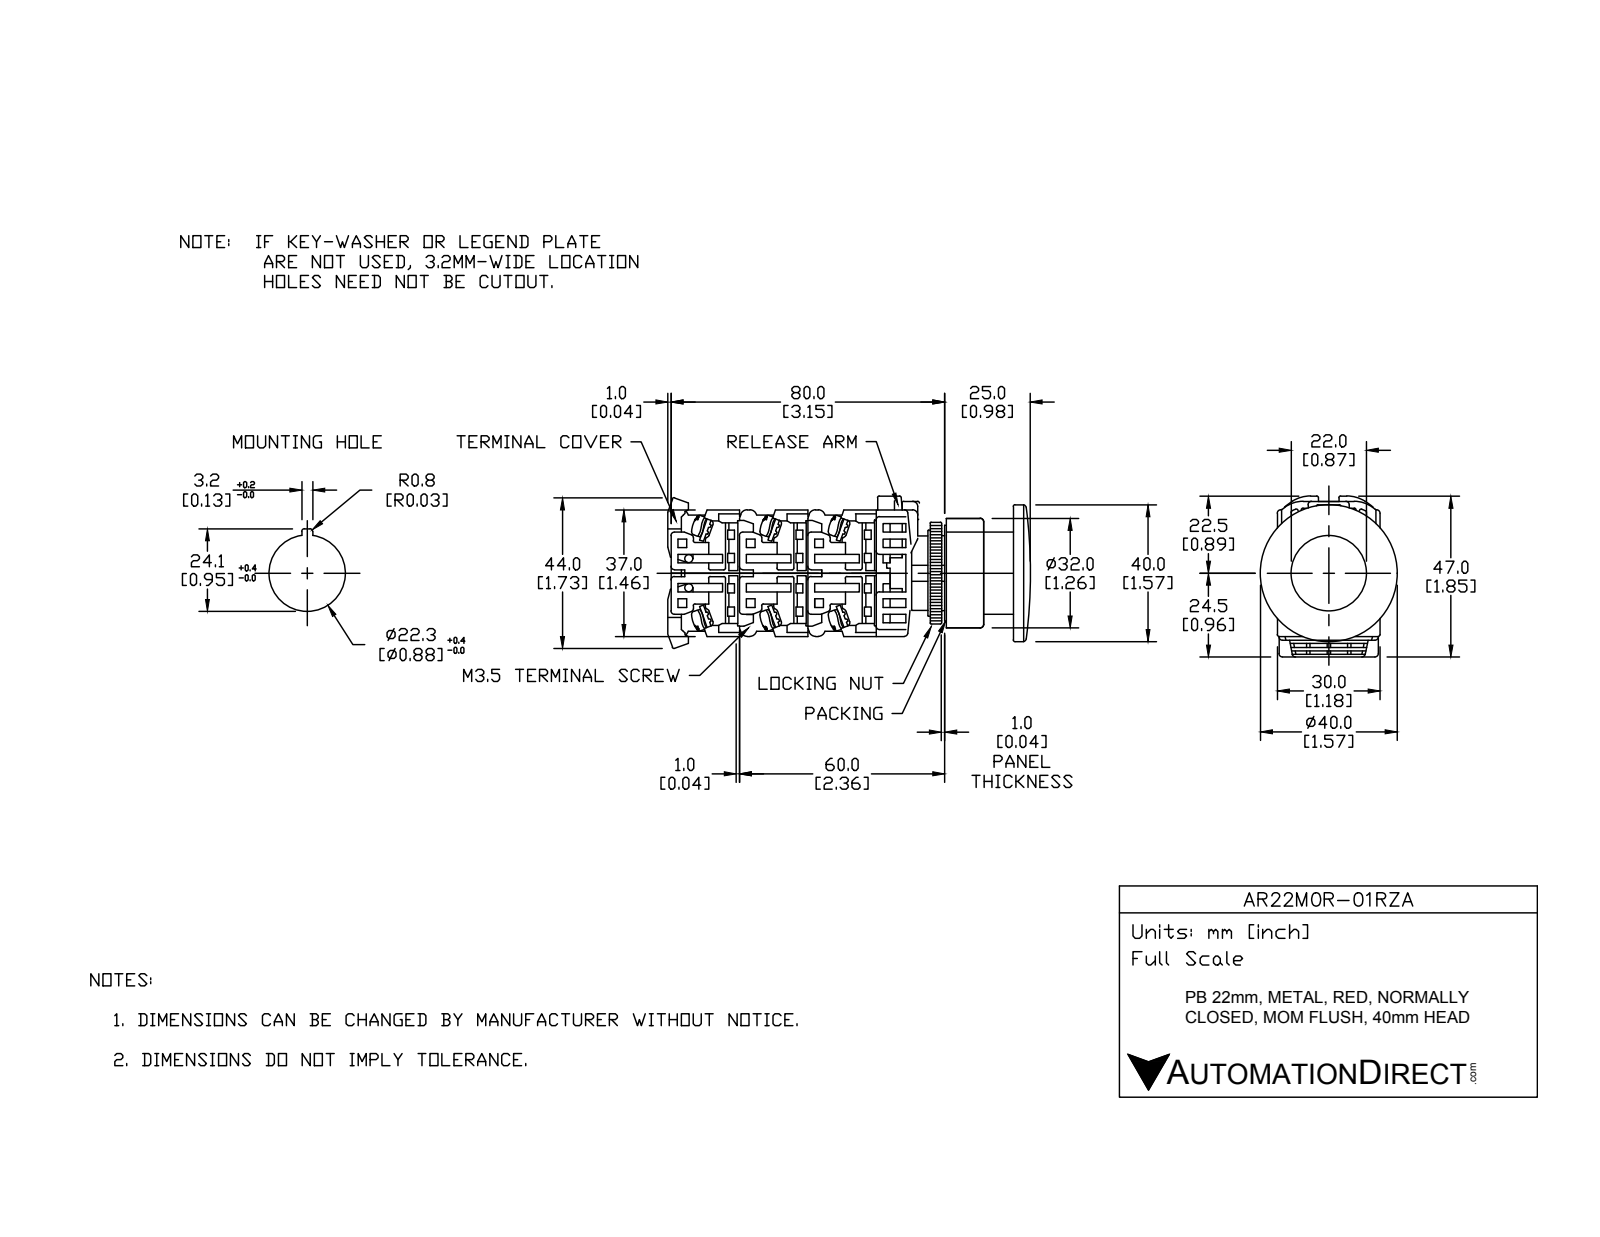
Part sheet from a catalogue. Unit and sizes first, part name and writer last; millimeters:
Units: millimetres
Overall size (bounding box): 66.5 × 43 × 40
Round holes (diameter × count): ⌀21.8 ×1, ⌀22 ×1, ⌀25 ×1, ⌀31 ×1
Round bosses / shafts (diameter × count): ⌀5 ×2, ⌀40 ×1, ⌀32 ×1, ⌀30.5 ×1, ⌀29.8 ×1, ⌀24 ×1, ⌀23.8 ×1, ⌀21.75 ×1
Partial cylindrical surfaces — rounded edges, fillets, slot ends (radius × count): R0.5 ×23, R1.75 ×4, R5 ×4, R4 ×2, R16.59 ×1, R17.59 ×1
Main face-to-face distances: 1, 10, 28.5, 18, 38.5, 21, 3, 2, 29, 7.5
Volume: 37 326 mm³ · Surface area: 22 079 mm²
Bodies: 12 solids, 304 faces (202 planar, 76 cylindrical, 26 other)
Part name (STEP PRODUCT): AR22M0R-01RZA
STEP written by: SolidWorks 2017 (AUTOMOTIVE_DESIGN)
